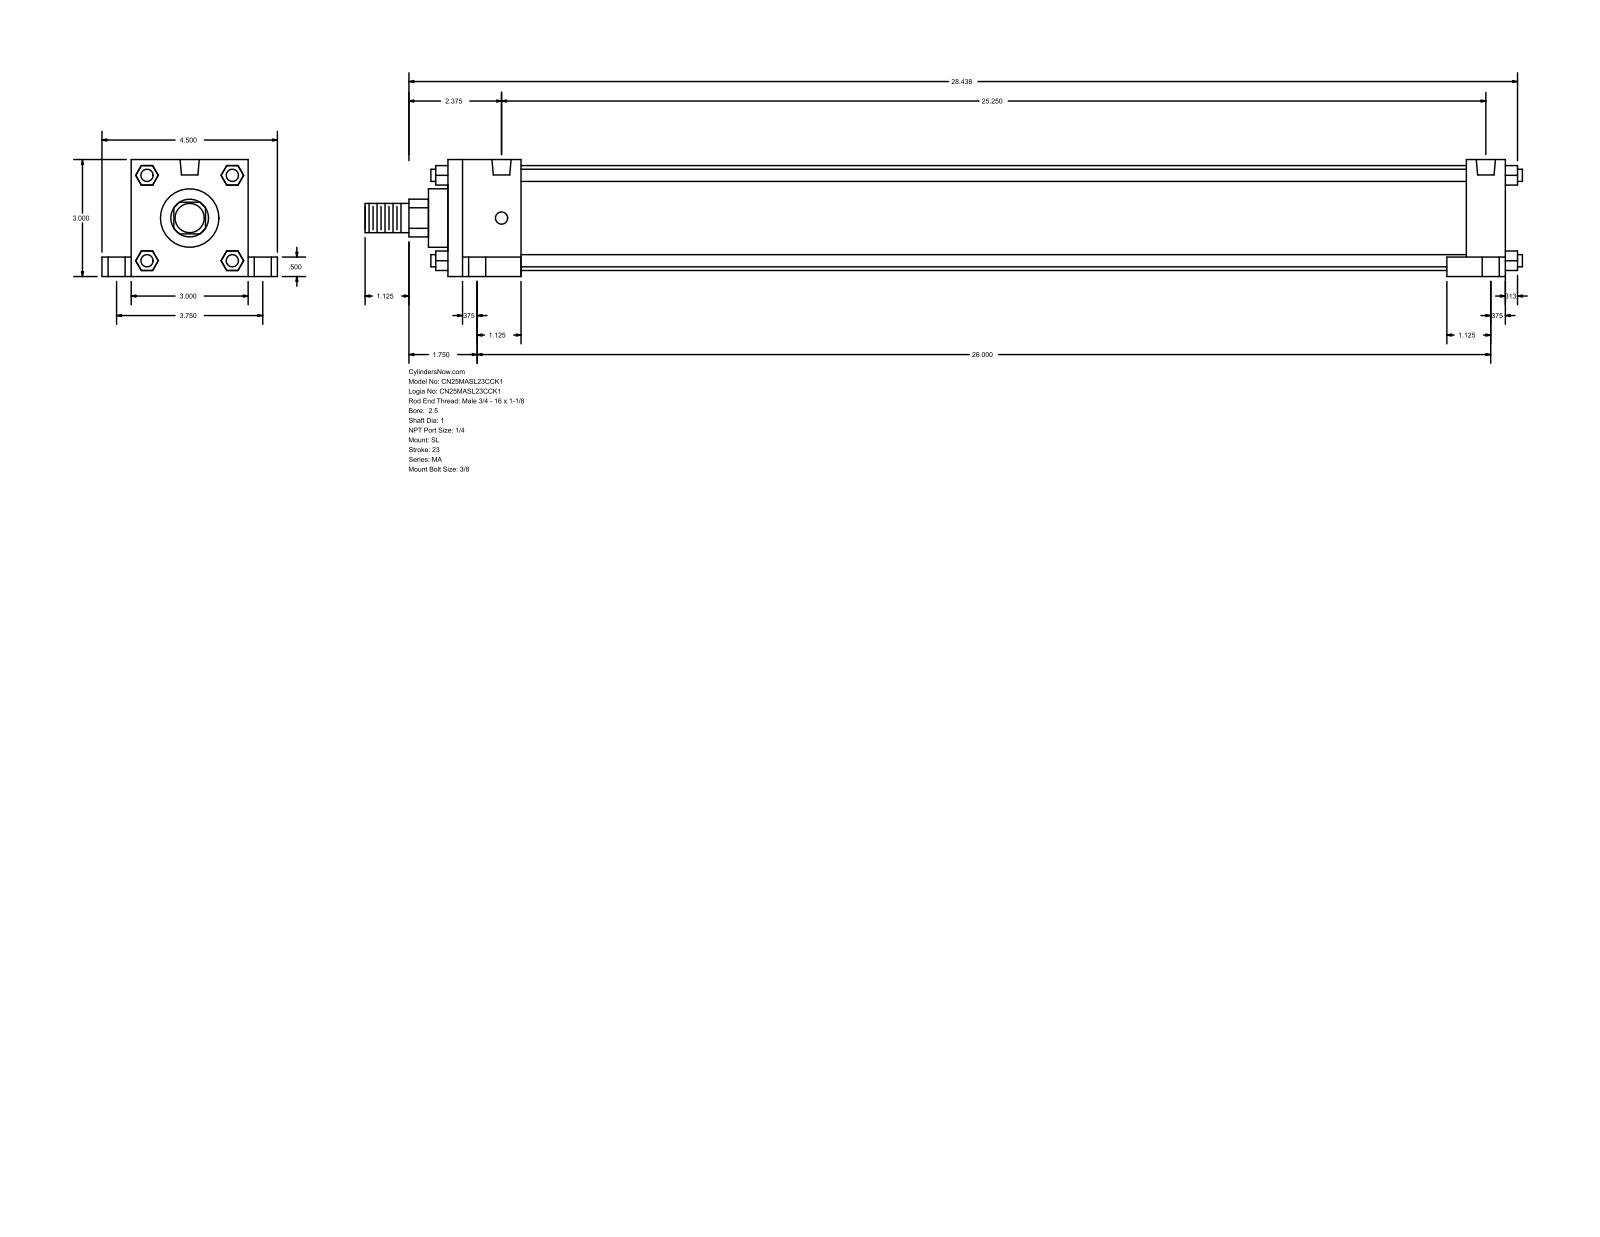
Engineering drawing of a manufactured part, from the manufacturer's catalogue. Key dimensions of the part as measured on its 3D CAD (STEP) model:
Part name (STEP PRODUCT): MA_SL__0250_1
STEP written by: GSSL Pune (CONFIG_CONTROL_DESIGN)
Units: millimetres
Bodies: 0 solids, 148 faces (112 planar, 36 cylindrical, 0 other)
Overall size (bounding box): 754.06 × 114.3 × 76.2
Round holes (diameter × count): ⌀7.94 ×4, ⌀11.11 ×4, ⌀17.46 ×4, ⌀12.49 ×2
Round bosses / shafts (diameter × count): ⌀7.94 ×4, ⌀68.33 ×1, ⌀38.1 ×1, ⌀25.4 ×1, ⌀19.05 ×1
Partial cylindrical surfaces — rounded edges, fillets, slot ends (radius × count): R12.29 ×1
Main face-to-face distances: 76.2, 688.98, 12.7, 615.95, 25.4, 47.63, 641.35, 663.58, 19.05, 95.25
Hole centre spacings: 47.73, 50.2, 95.24, 641.34, 646.28, 658.94, 660.4, 667.23
